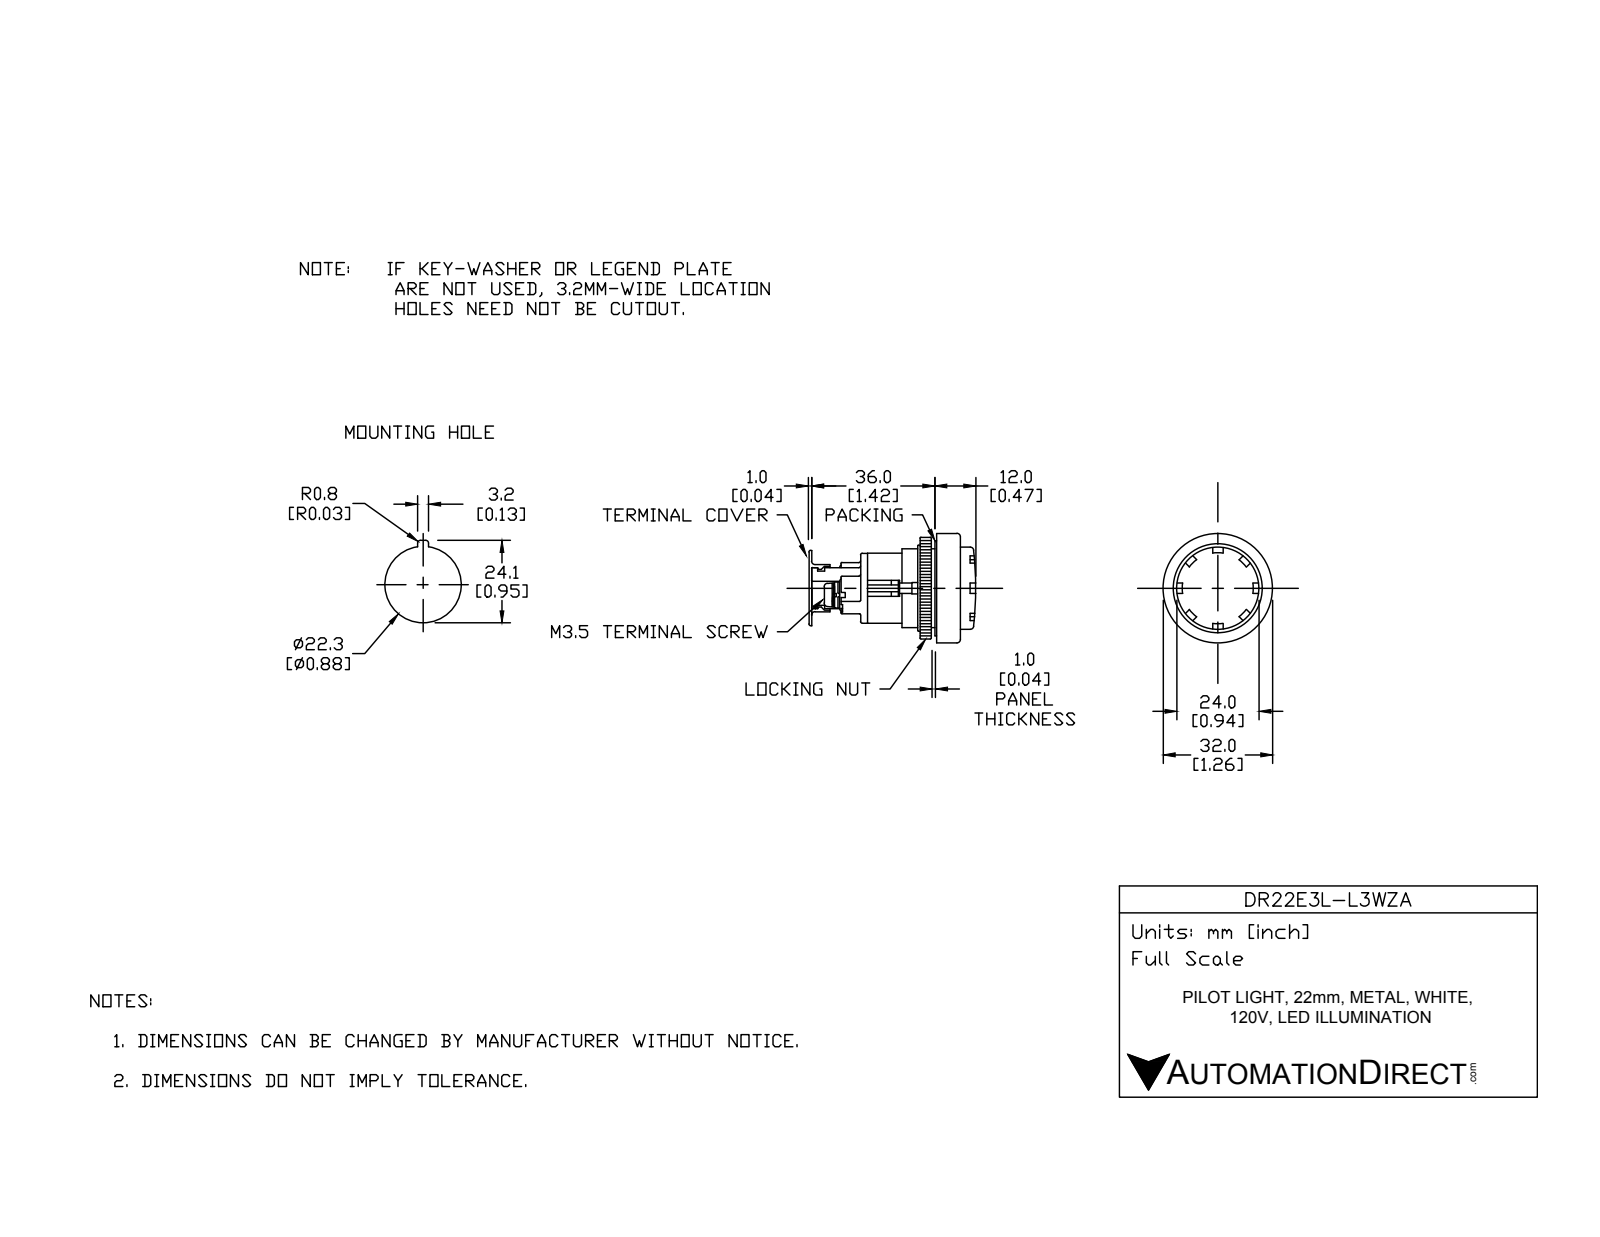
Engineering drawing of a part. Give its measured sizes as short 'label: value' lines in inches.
name: DR22E3L-L3WZA
written by: SolidWorks 2017 (AUTOMOTIVE_DESIGN)
unit: in
bodies: 12 solids, 232 faces (165 planar, 51 cylindrical, 16 other)
size: 2.913 × 1.26 × 1.26
volume: 2.435 in³; area: 28.15 in²
holes: 1× ⌀0.866, 1× ⌀0.886, 1× ⌀0.984, 1× ⌀1.181
bosses: 2× ⌀0.217, 1× ⌀1.26, 1× ⌀1.169, 1× ⌀1.161, 1× ⌀1.063, 1× ⌀0.858
rounds: 14× R0.02, 4× R0.128, 1× R0.039, 1× R0.197
face distances: 0.748, 1.181, 1.055, 0.039, 0.157, 0.236, 0.819, 0.433, 1.28, 0.063
